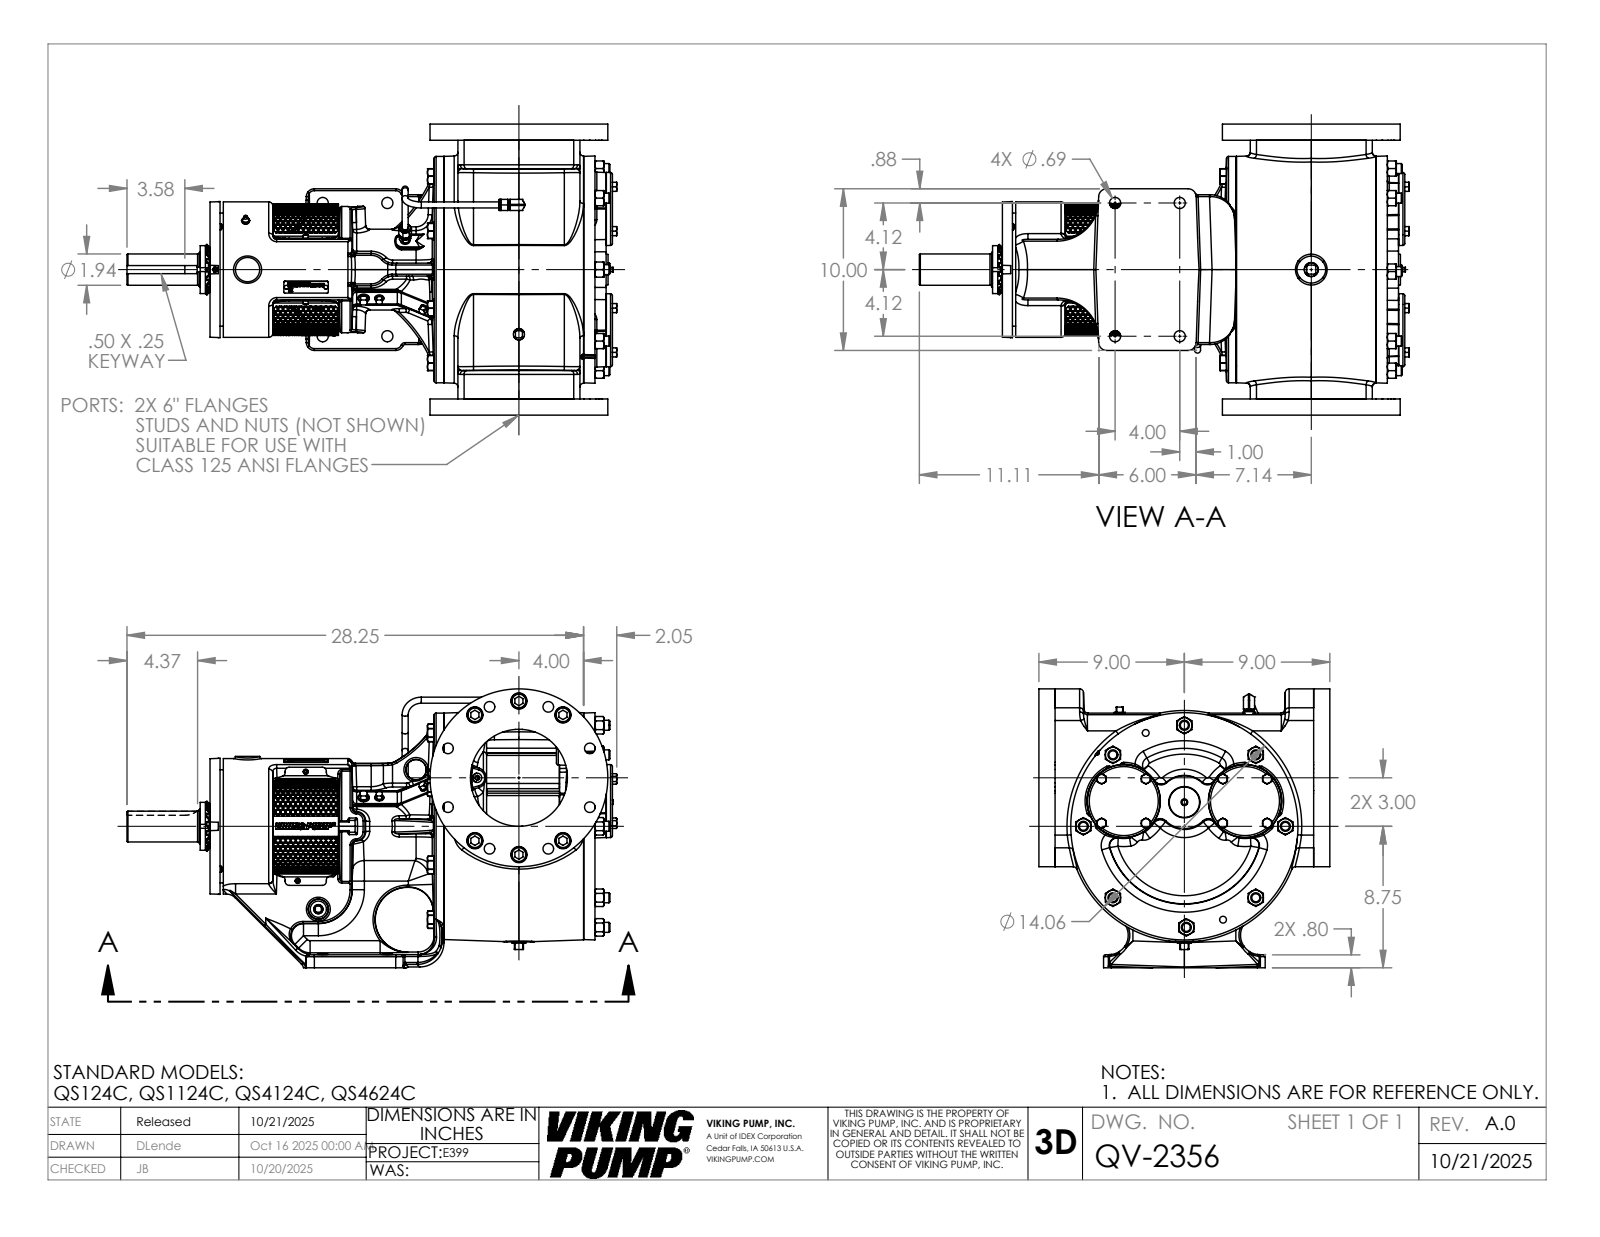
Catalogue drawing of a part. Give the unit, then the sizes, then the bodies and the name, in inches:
Units: inches
Overall size (bounding box): 30.304 × 18 × 17.25
Round holes (diameter × count): ⌀0.25 ×9, ⌀0.266 ×8, ⌀0.656 ×8, ⌀1.157 ×8, ⌀1 ×6, ⌀0.688 ×4, ⌀0.875 ×4, ⌀0.159 ×2, ⌀0.313 ×2, ⌀0.422 ×2, ⌀0.453 ×1, ⌀2.157 ×1
Round bosses / shafts (diameter × count): ⌀0.617 ×8, ⌀0.937 ×6, ⌀0.375 ×5, ⌀0.312 ×3, ⌀0.19 ×3, ⌀4.5 ×2, ⌀0.687 ×2, ⌀0.563 ×2
Partial cylindrical surfaces — rounded edges, fillets, slot ends (radius × count): R0.12 ×60, R0.25 ×22, R0.015 ×18, R0.092 ×18, R0.07 ×16, R0.75 ×14, R0.5 ×13, R1 ×9
Main face-to-face distances: 18, 1, 17, 0.57, 23.817, 3.82, 19.998, 0.898, 17.118, 16.22
Hole centre spacings: 3.75, 2.079, 4.75, 5.783, 2.713, 3.133, 3.788, 5.423
Volume: 2 567 in³ · Surface area: 2 332 in²
Bodies: 1 solid, 4171 faces (1410 planar, 676 cylindrical, 2085 other)
Part name (STEP PRODUCT): QV-2356
STEP written by: SolidWorks 2024 (AUTOMOTIVE_DESIGN)
